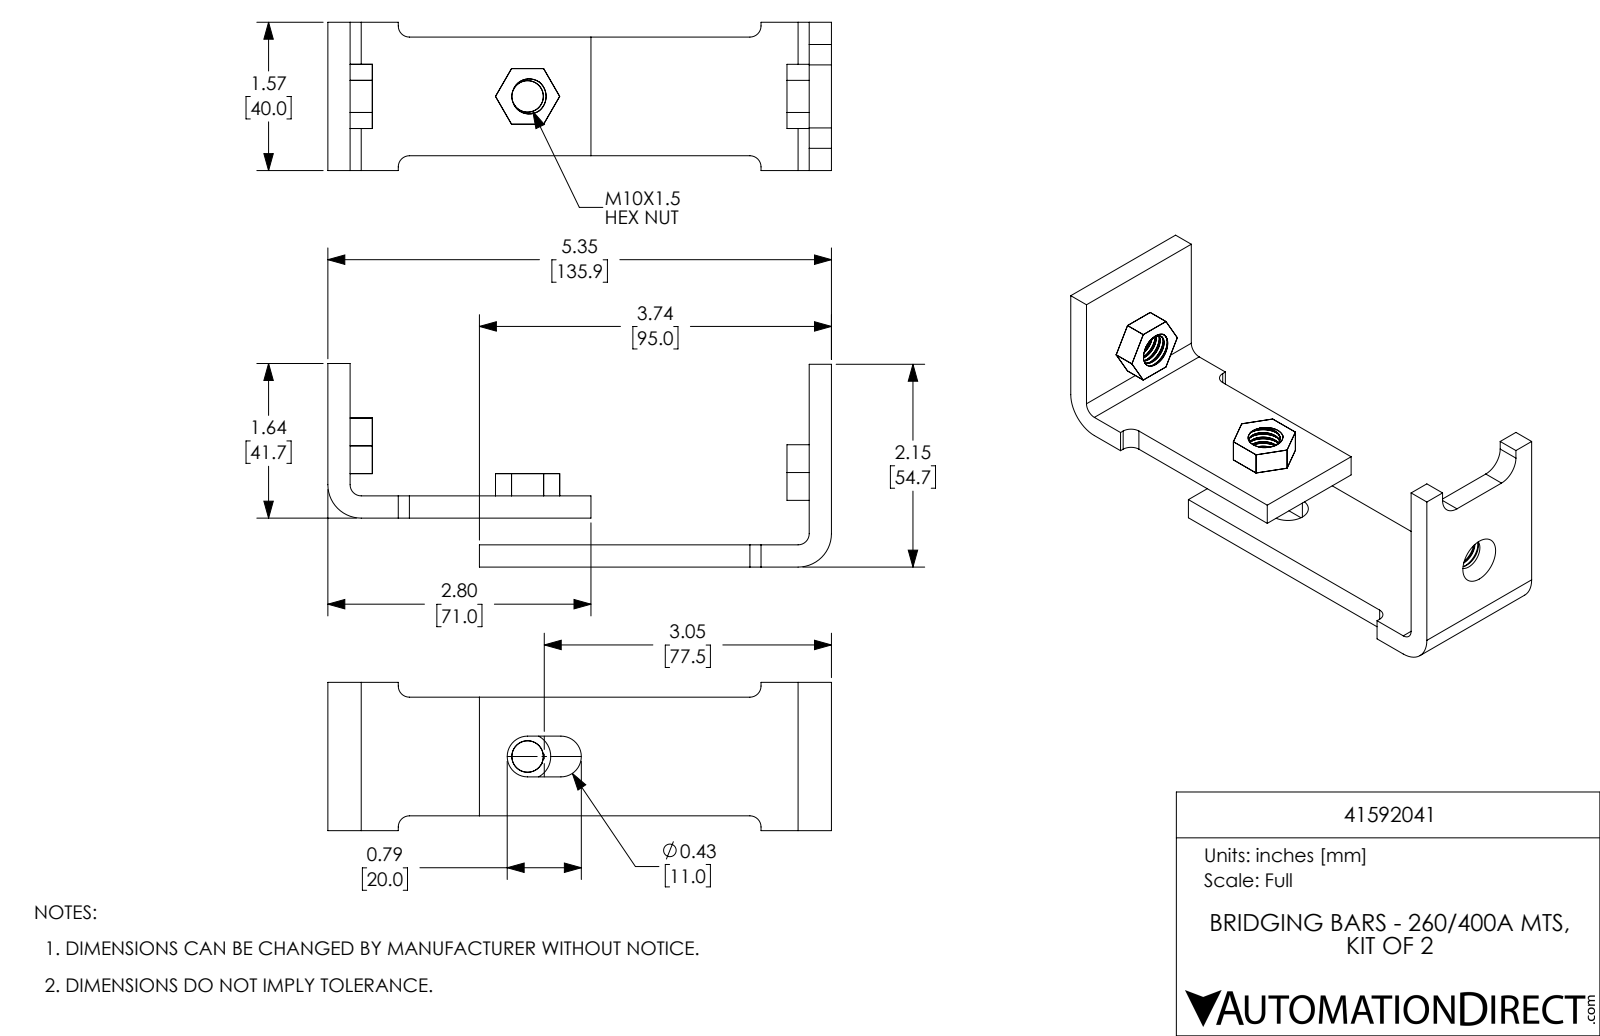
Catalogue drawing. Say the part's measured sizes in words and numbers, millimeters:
The part is named "41592041". Its 3-D file was written by "SolidWorks 2017 (AUTOMOTIVE_DESIGN)". It is 7 solids with 233 faces: 80 planar, 143 cylindrical and 10 other. Overall it measures 135.9 by 54.9 by 40 millimeters. Its volume is 52 570 cubic millimeters and its surface area 26 080 square millimeters. Round holes: 3 of diameter 8.5, 3 of diameter 10, 3 of diameter 12.5. Round bosses or shafts: 3 of diameter 13. Partial cylindrical surfaces (rounded edges, fillets, slot ends): 6 of radius 3, 4 of radius 5.5, 2 of radius 9. The main face-to-face distances are 6, 13.2, 129.9, 19.2, 7.2, 4, 123.9, 36, 135.9, 15. The hole center spacings are 7.2.
